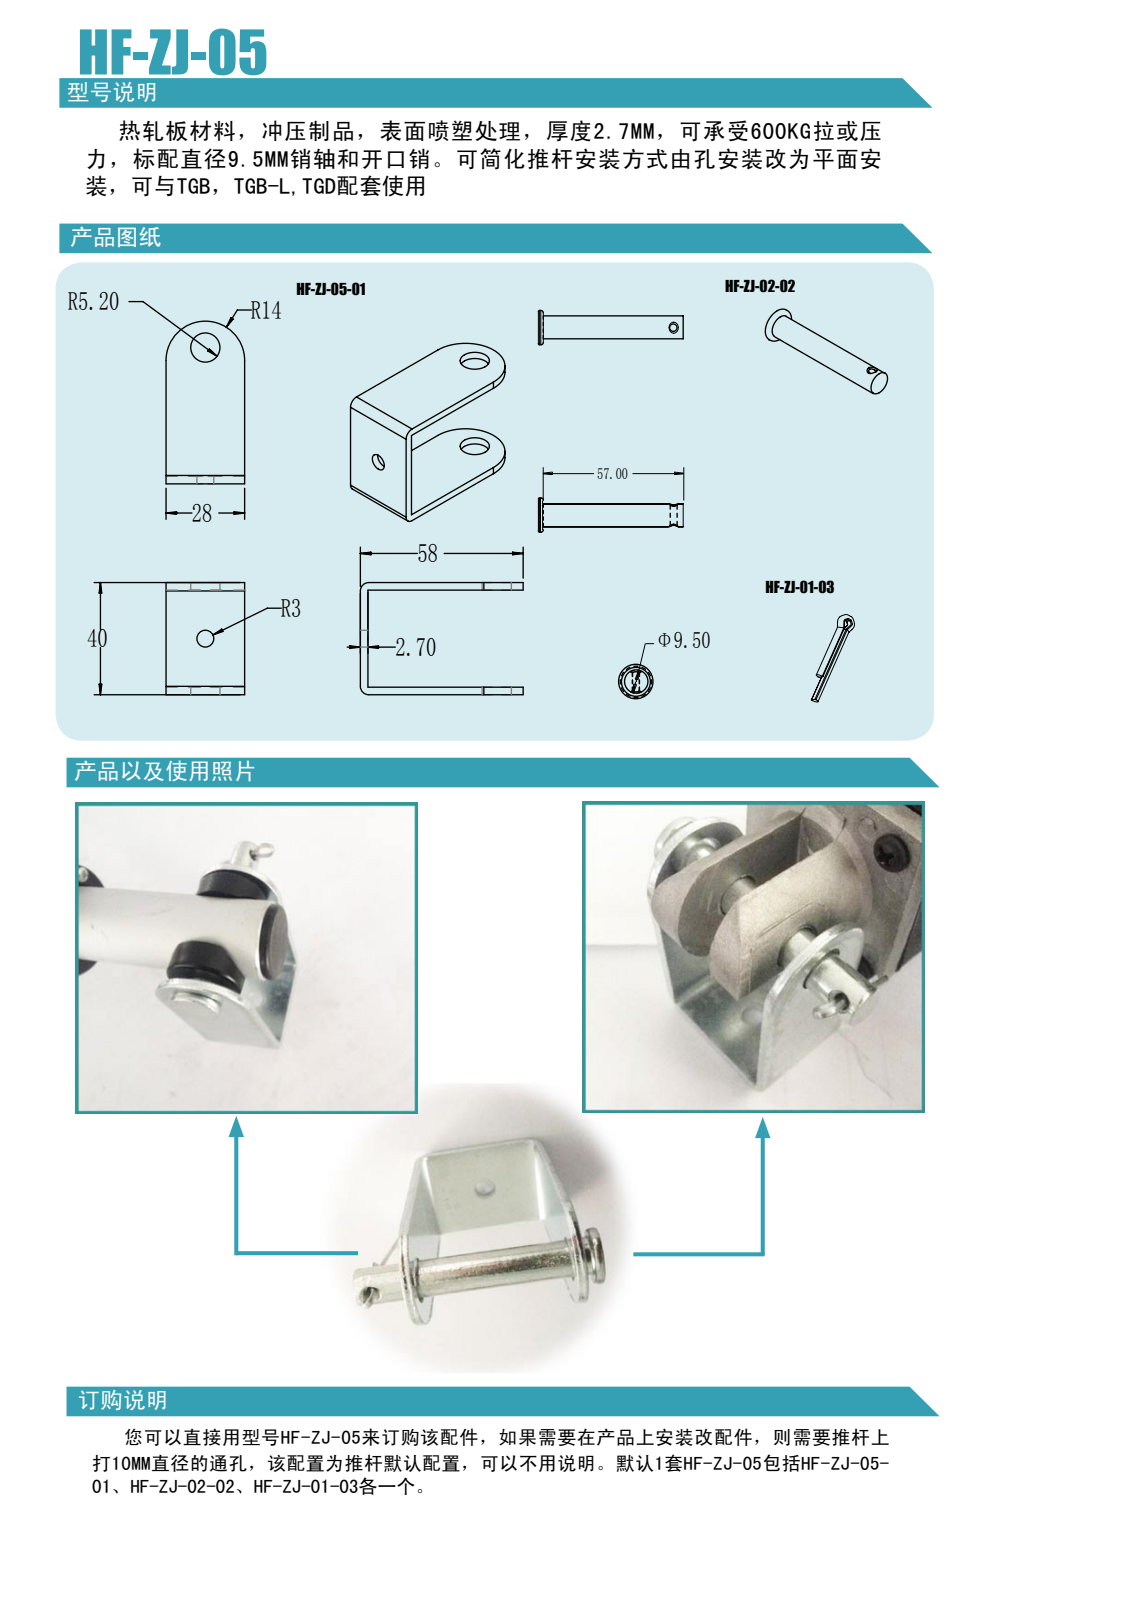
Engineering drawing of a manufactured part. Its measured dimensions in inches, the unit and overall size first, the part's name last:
Units: inches
Overall size (bounding box): 58 × 40 × 28
Round holes (diameter × count): ⌀6 ×1, ⌀10.4 ×1
Partial cylindrical surfaces — rounded edges, fillets, slot ends (radius × count): R3 ×2, R14 ×1
Main face-to-face distances: 2.7, 37.3, 34.6, 40, 28
Volume: 10 288 in³ · Surface area: 8 748 in²
Bodies: 1 solid, 18 faces (8 planar, 10 cylindrical, 0 other)
Part name (STEP PRODUCT): ZJ-05
STEP written by: PRO/ENGINEER BY PARAMETRIC TECHNOLOGY CORPORATION, 2008380 (CONFIG_CONTROL_DESIGN)
